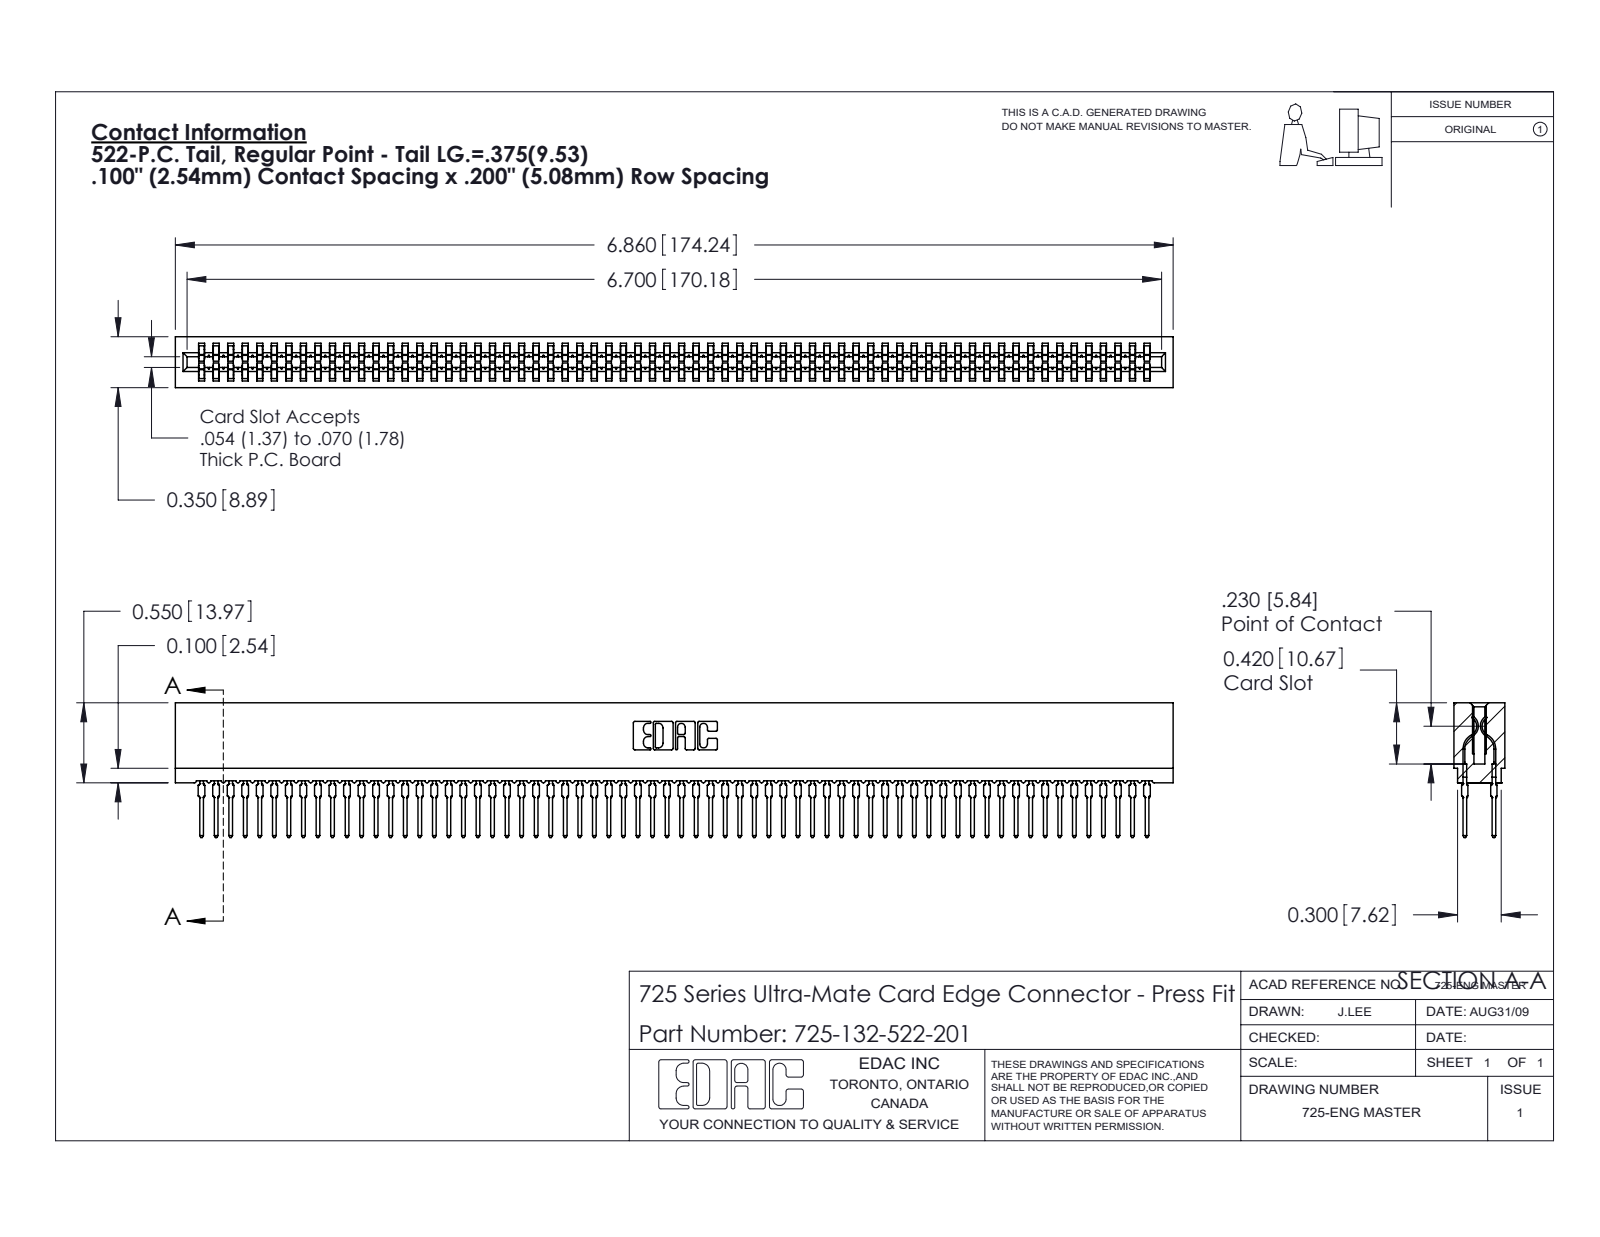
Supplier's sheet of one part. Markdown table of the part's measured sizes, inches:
| quantity | value |
| --- | --- |
| part name | 745-292-001_522; 725-132-522-201; 725 Part_Insulator Option - 01 |
| STEP written by | SolidWorks 2020 (CONFIG_CONTROL_DESIGN) |
| units | inches |
| bodies | 133 solids, 11909 faces (6127 planar, 2350 cylindrical, 3432 other) |
| overall size | 6.86 × 0.926 × 0.35 |
| volume | 0.844 in³ |
| surface area | 46.85 in² |
| partial cylindrical surfaces (radius × count) | 0.021 × 264, 0.015 × 132, 0.01 × 22, 0.005 × 8, 0.011 × 8, 0.007 × 6, 0.031 × 6, 0.026 × 3 |
| main face-to-face distances | 0.063, 0.287, 0.2, 0.35, 0.212, 0.138, 0.076, 0.149, 0.045, 0.305 |
